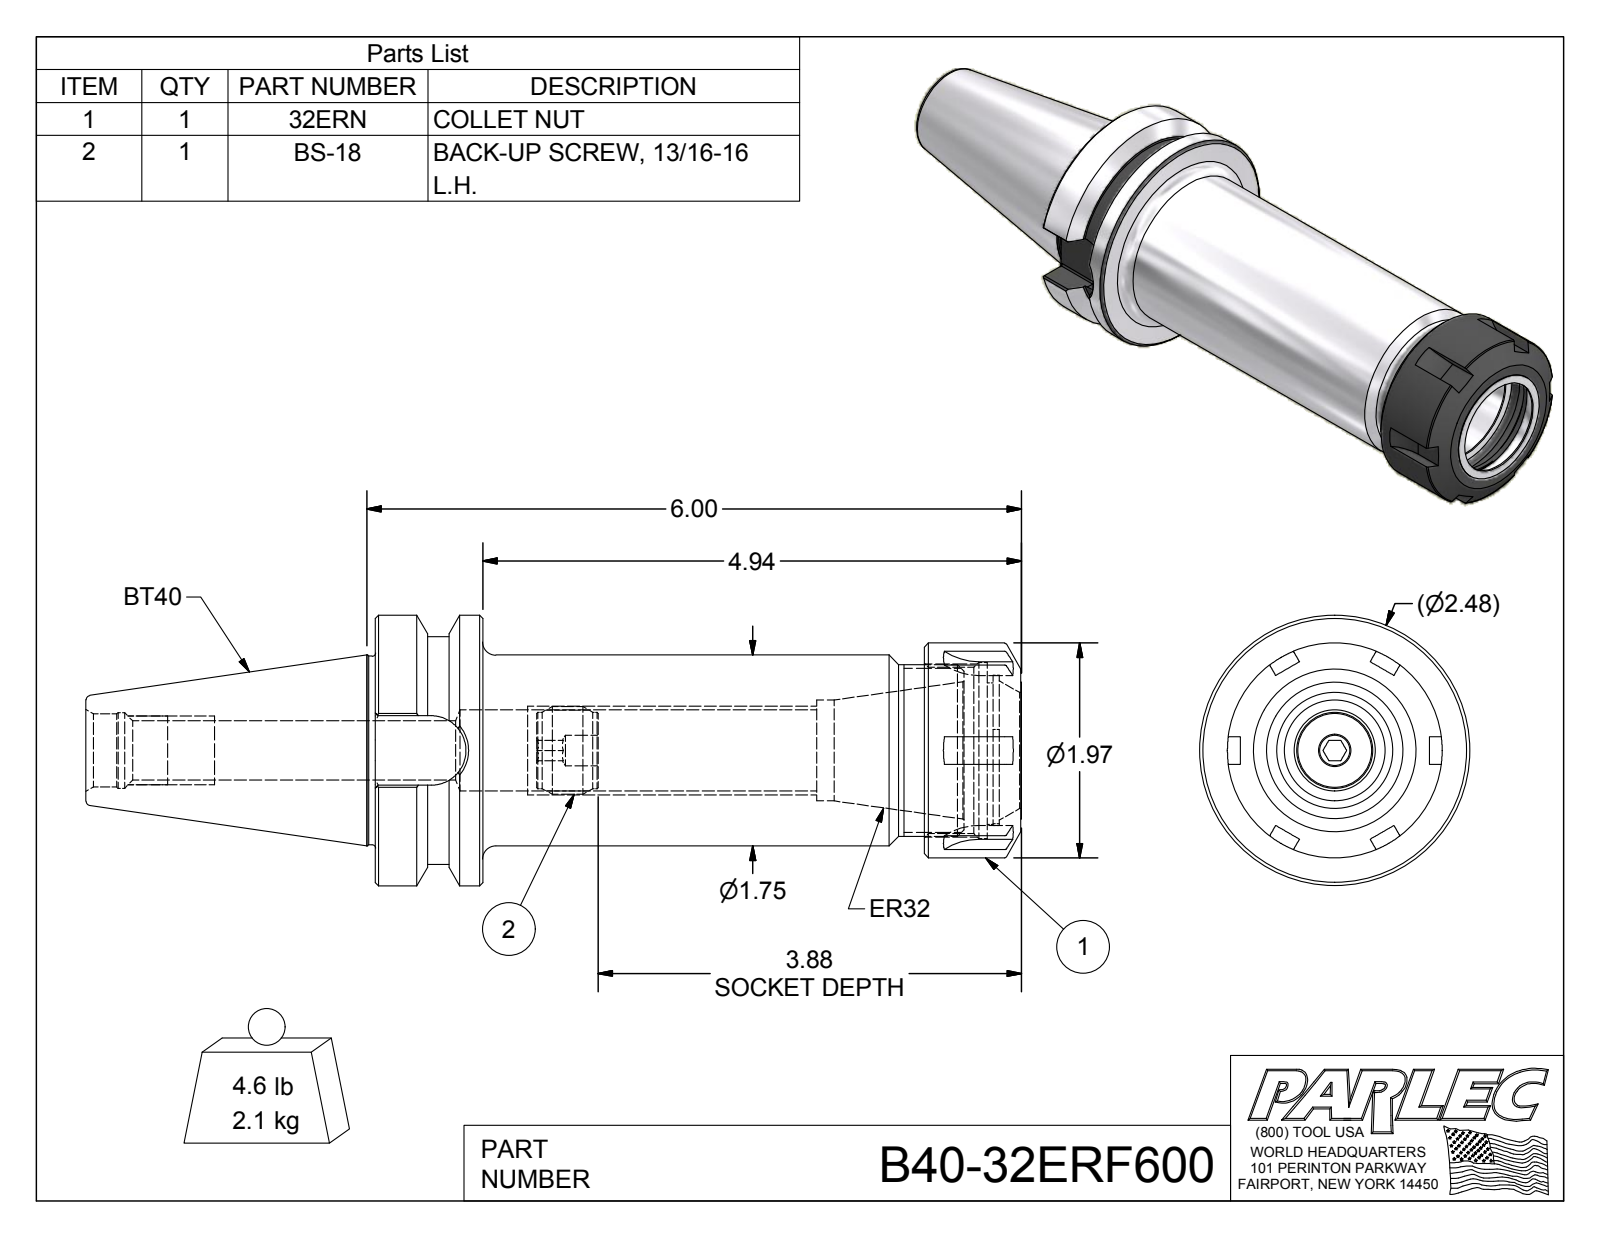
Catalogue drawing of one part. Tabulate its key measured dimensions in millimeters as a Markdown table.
| quantity | value |
| --- | --- |
| part name | B40-32ER6-1; 32ERN; BS-18; B40-32ERF600 |
| STEP written by | Autodesk Inventor 2016 (AUTOMOTIVE_DESIGN) |
| units | millimeters |
| bodies | 3 solids, 173 faces (67 planar, 46 cylindrical, 60 other) |
| overall size | 217.81 × 62.99 × 62.99 |
| volume | 267 666 mm³ |
| surface area | 55 089 mm² |
| round holes (diameter × count) | 7.11 × 1, 13.84 × 1, 17.01 × 1, 17.62 × 1, 18.92 × 1, 23.5 × 1, 27 × 1, 33.02 × 1, 38.65 × 1, 41 × 1 |
| round bosses / shafts (diameter × count) | 62.99 × 1, 53.01 × 1, 50 × 1, 44.45 × 1, 43.94 × 1, 40 × 1, 20.45 × 1, 17.78 × 1 |
| partial cylindrical surfaces (radius × count) | 0.51 × 20, 8.09 × 1, 14.9 × 1, 17.5 × 1 |
| main face-to-face distances | 24.99, 150.42, 125.43, 127.64, 102.65, 22.78, 142.65, 117.66, 15.01, 7.77 |
| hole center spacings | 1.86 |
